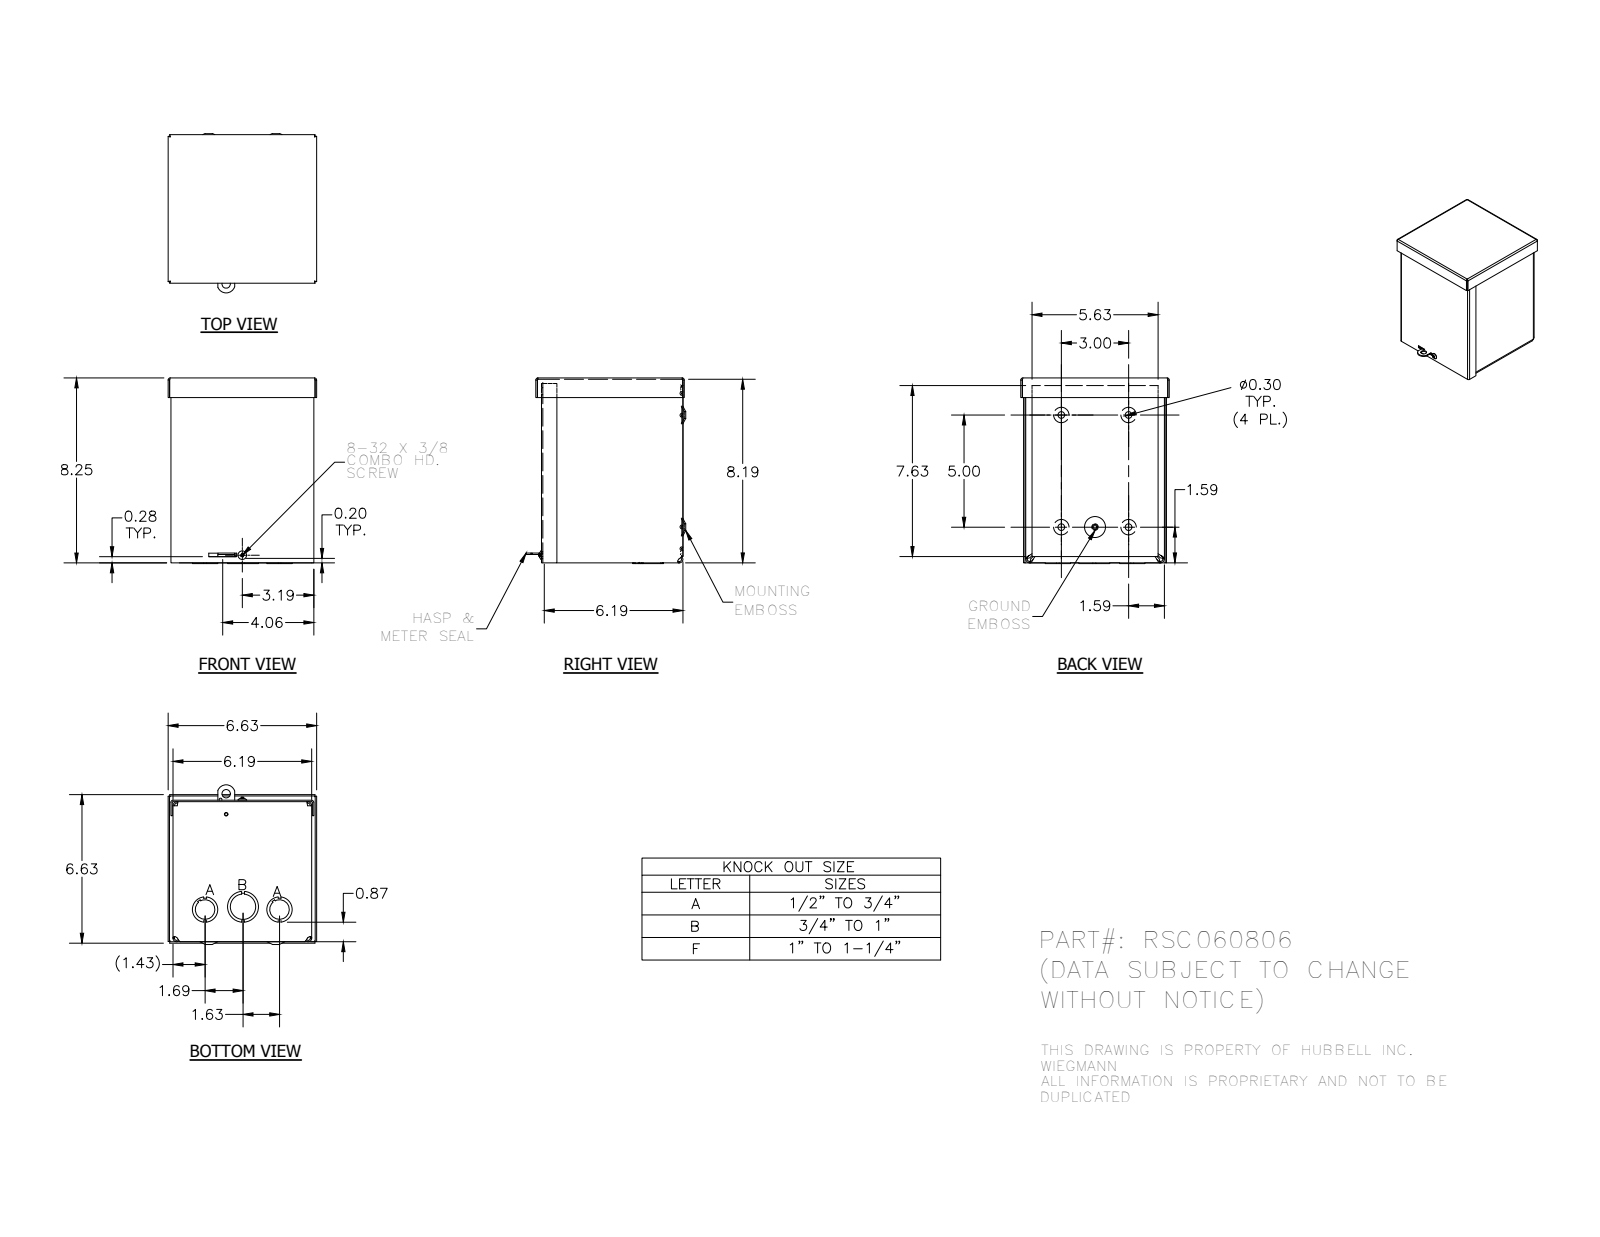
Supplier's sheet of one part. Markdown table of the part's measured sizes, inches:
| quantity | value |
| --- | --- |
| part name | RSC060806; RSC060806_WRAP; RSC0608_LID; RSC0606_CAP (+4 more) |
| STEP written by | Autodesk Inventor 2012 (AUTOMOTIVE_DESIGN) |
| units | inches |
| bodies | 6 solids, 461 faces (220 planar, 116 cylindrical, 125 other) |
| overall size | 8.281 × 7.125 × 6.625 |
| volume | 23.68 in³ |
| surface area | 776.9 in² |
| round holes (diameter × count) | 0.3 × 4, 1.125 × 3, 0.125 × 2, 0.313 × 2, 0.875 × 2, 0.148 × 1, 0.156 × 1, 0.165 × 1, 0.375 × 1, 1.375 × 1 |
| round bosses / shafts (diameter × count) | 0.384 × 1, 0.229 × 1, 0.164 × 1 |
| partial cylindrical surfaces (radius × count) | 0.01 × 10, 0.031 × 8, 0.093 × 8, 0.125 × 8, 0.187 × 8, 0.021 × 4, 0.031 × 4, 0.055 × 4 |
| main face-to-face distances | 0.062, 0.062, 6.126, 8.126, 6.249, 6.188, 6.063, 0.124, 6.187, 0.063 |
| hole center spacings | 1.5, 3, 5, 5.22, 5.831, 0.358, 0.702, 0.913 |
